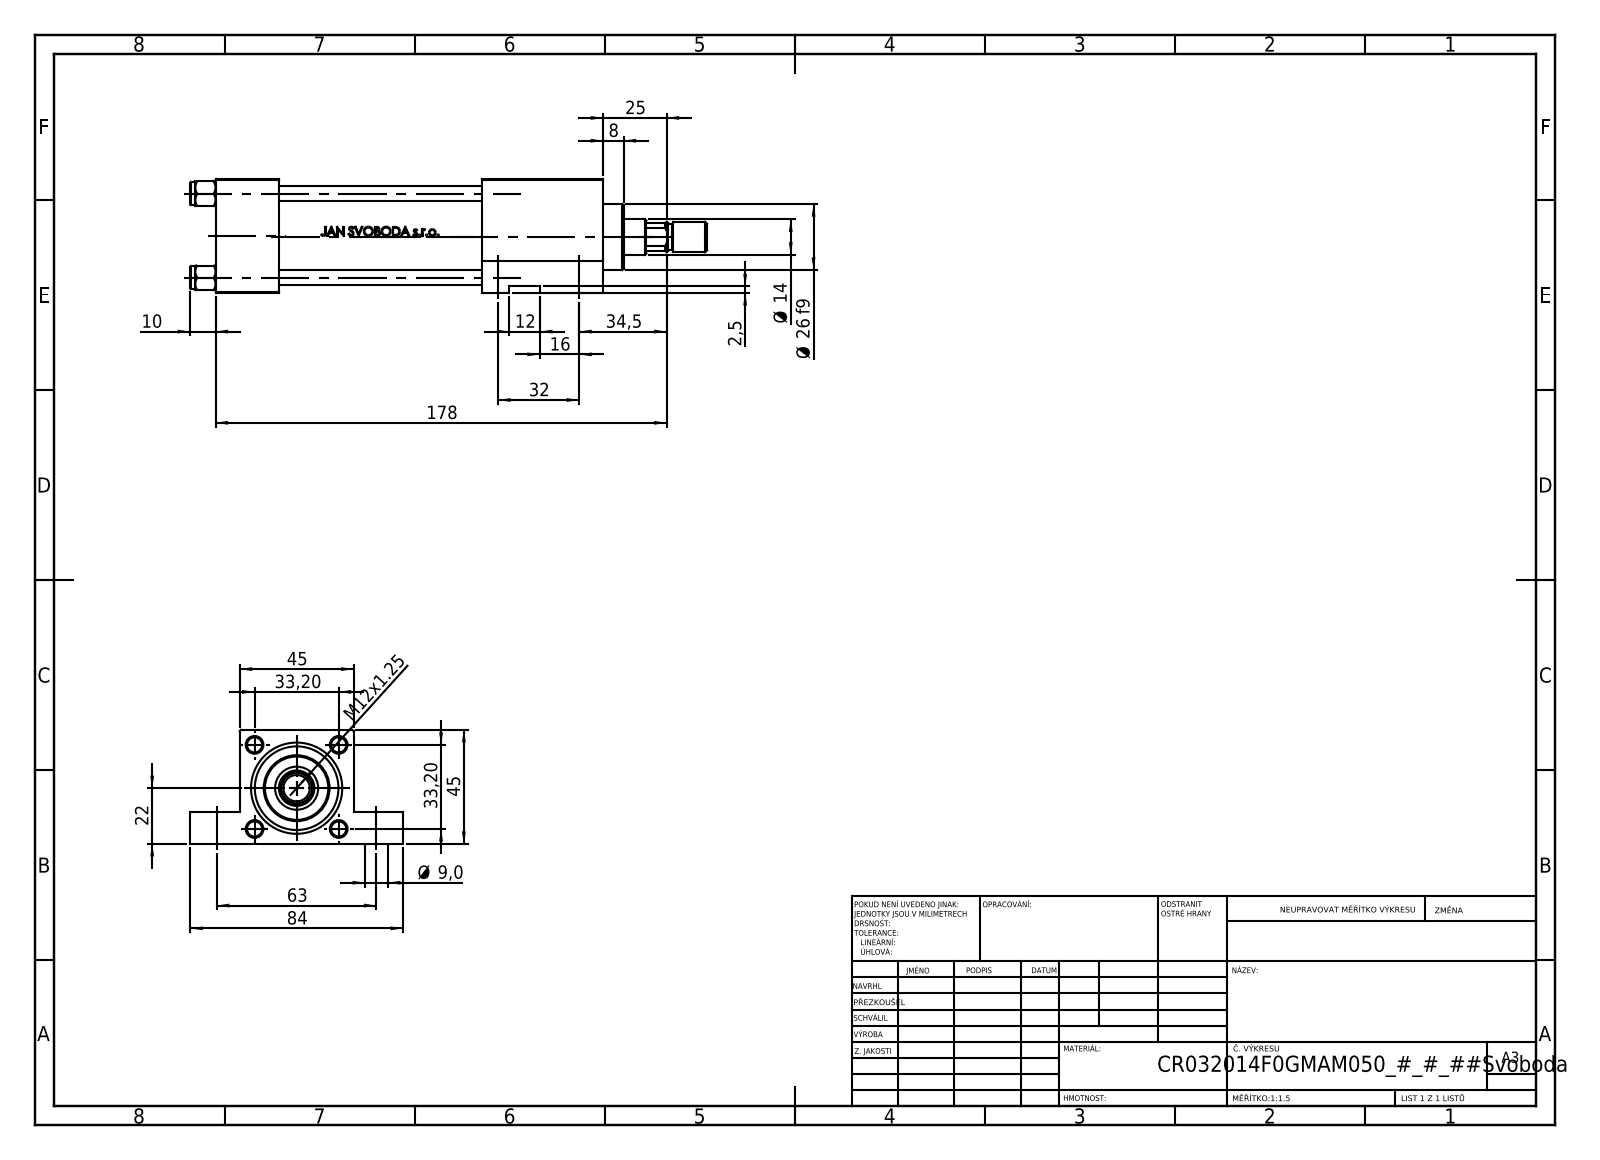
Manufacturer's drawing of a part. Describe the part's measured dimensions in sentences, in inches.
The part is named "V215CR_F_Body; V215_VC_A; V215CR_VCP_F; ROD_END_AH (+2 more)". Its 3-D file was written by "SolidWorks 2019 (CONFIG_CONTROL_DESIGN)". It is 12 solids with 1116 faces: 440 planar, 130 cylindrical and 546 other. Overall it measures 8.031 by 3.307 by 1.772 inches. Its volume is 14.13 cubic inches and its surface area 129.8 square inches. Round holes: 4 of diameter 0.236, 2 of diameter 0.276, 2 of diameter 0.354, 2 of diameter 0.354, 2 of diameter 0.787, 1 of diameter 0.256, 1 of diameter 0.512, 1 of diameter 0.518, 1 of diameter 0.551, 1 of diameter 0.669, 1 of diameter 0.945, 1 of diameter 1.26. Round bosses or shafts: 4 of diameter 0.354, 1 of diameter 1.496, 1 of diameter 1.024, 1 of diameter 0.472, 1 of diameter 0.394. Partial cylindrical surfaces (rounded edges, fillets, slot ends): 1 of radius 0.256. The main face-to-face distances are 1.772, 0.984, 5.039, 6.024, 1.28, 4.134, 3.15, 1.89, 0.492, 0.394. The hole center spacings are 1.307, 0.911, 0.938, 1.26, 1.848, 2.48, 2.782, 4.154.
